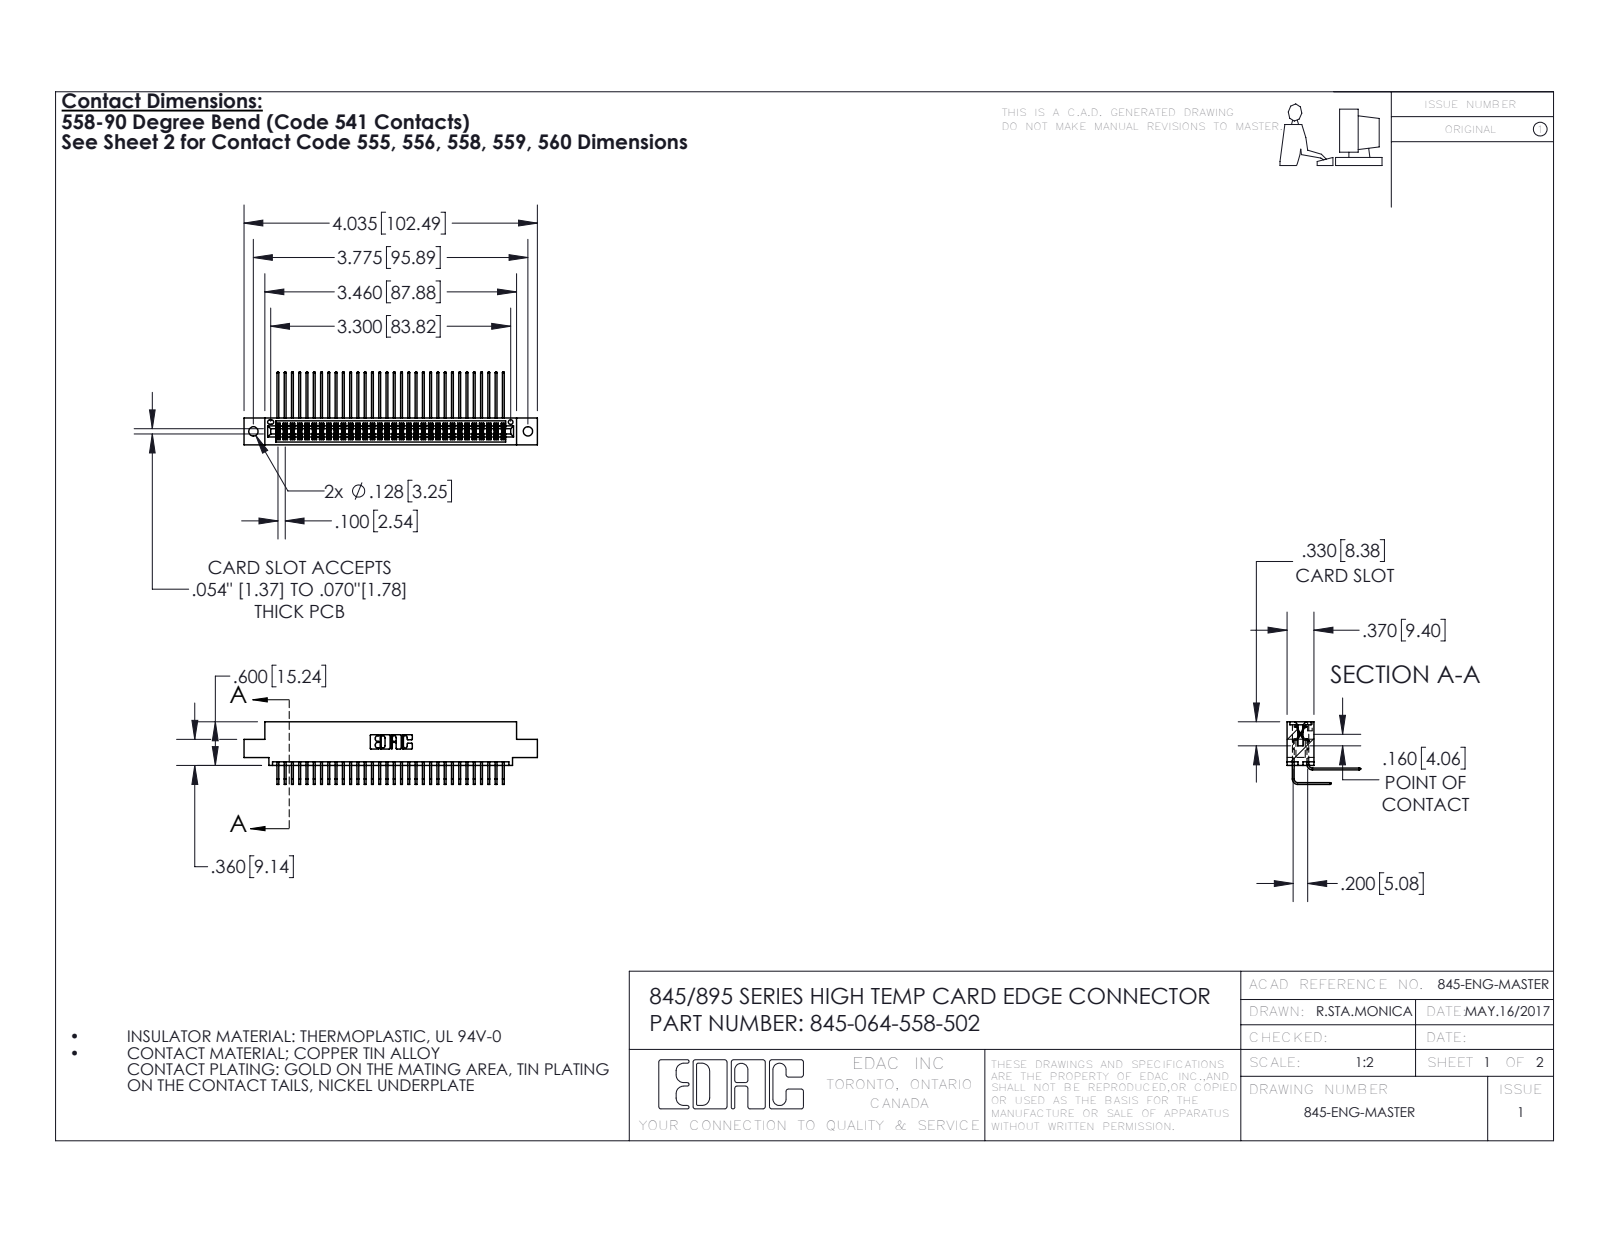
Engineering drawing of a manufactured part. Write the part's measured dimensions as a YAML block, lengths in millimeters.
part_name: "345 Part_0.110 Offset - 0.128 Dia; 345-292-001_558 Tail - 2; 345-292-001_558 559 Tail - 1; 345-064-558-502"
step_written_by: "SolidWorks 2016 (CONFIG_CONTROL_DESIGN)"
units: millimeters
bodies: {solids: 65, faces: 3458, planar: 2324, cylindrical: 1134, other: 0}
overall_size: [102.5, 25.5, 21.8]
volume: 10100
surface_area: 16320
round_holes:
  - {diameter: 3.3, count: 2}
  - {diameter: 1.6, count: 1}
partial_cylinders:
  - {radius: 0.2, count: 128}
  - {radius: 0.3, count: 22}
  - {radius: 0.2, count: 6}
  - {radius: 0.8, count: 6}
  - {radius: 0.7, count: 3}
  - {radius: 0.4, count: 2}
  - {radius: 0.5, count: 2}
  - {radius: 0.6, count: 2}
face_to_face_distances: [1.8, 7.6, 5.1, 9.4, 2.5, 6.9, 0.6, 5.7, 0.6, 4.4]
hole_center_spacings: [6.9, 89.9, 95.9]
